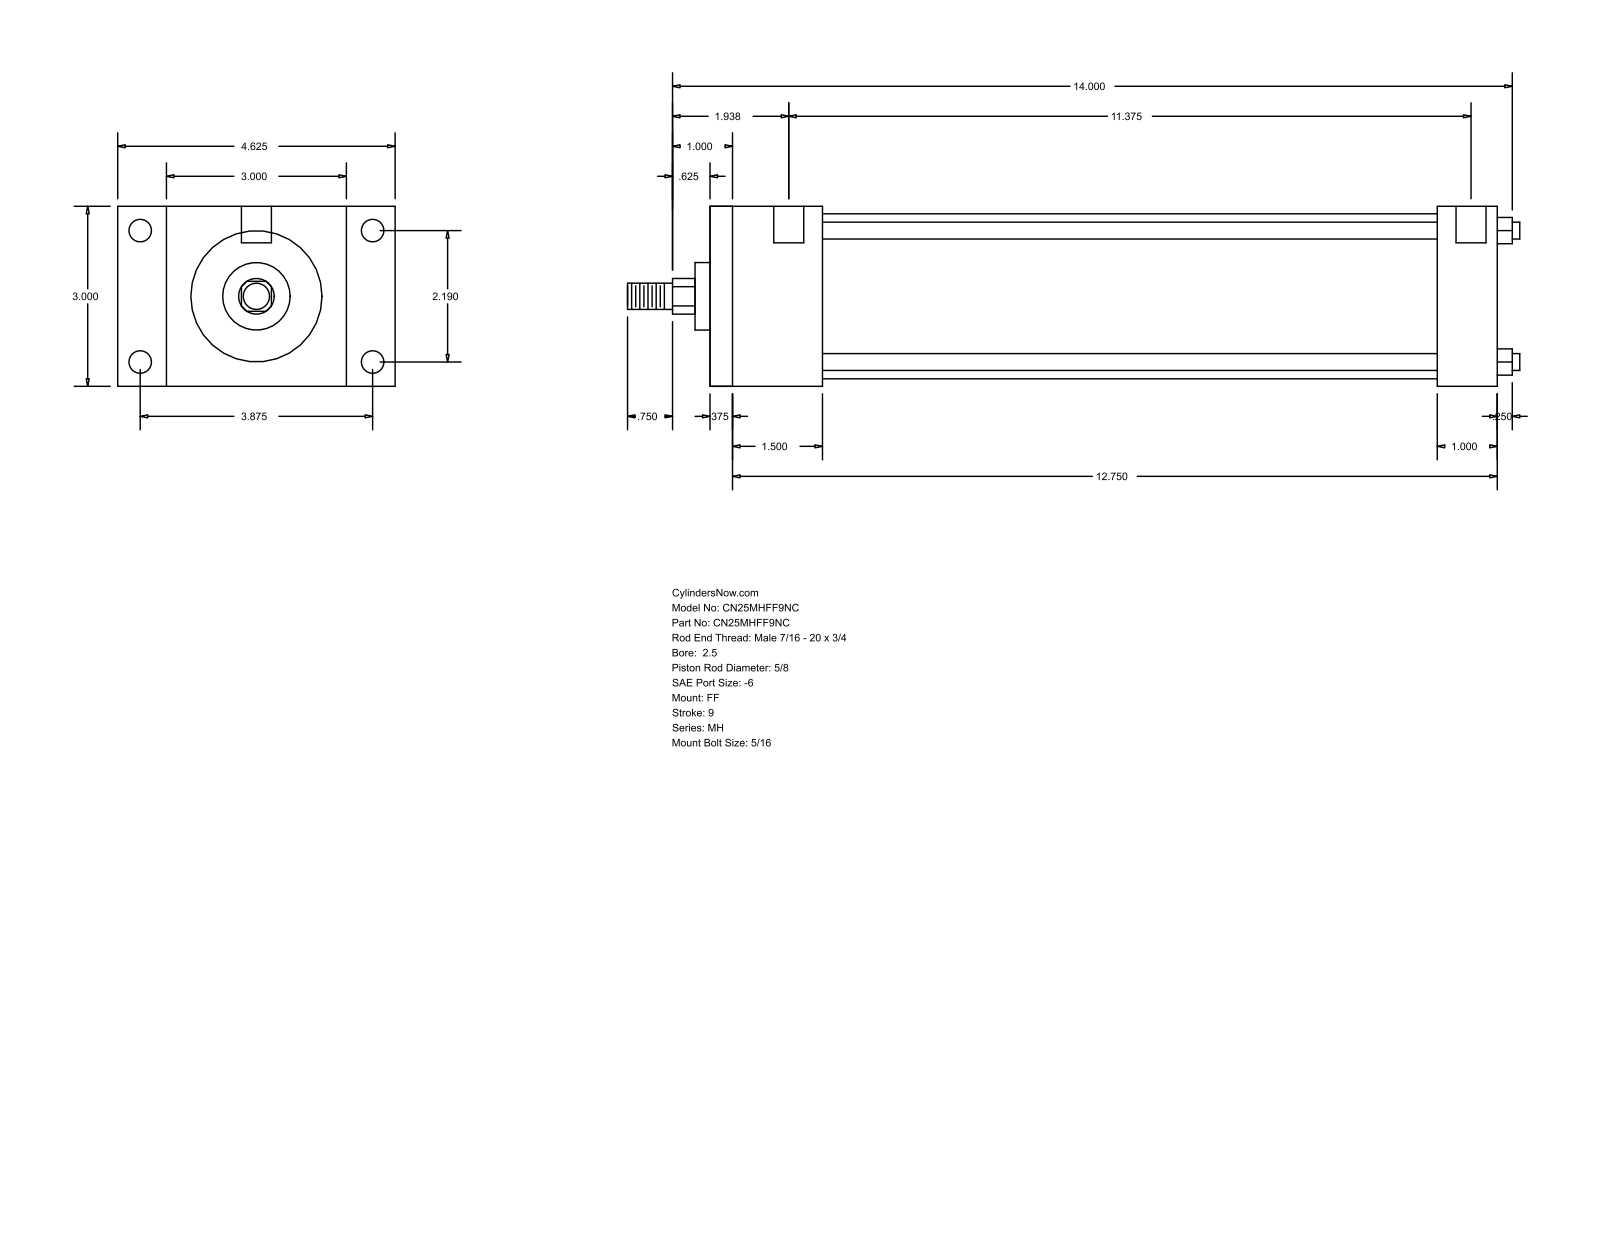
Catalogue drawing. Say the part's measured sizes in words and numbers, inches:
The part is named "MH_FF__0250_0.625". Its 3-D file was written by "GSSL Pune (CONFIG_CONTROL_DESIGN)". It is 0 solids with 92 faces: 64 planar, 28 cylindrical and 0 other. Overall it measures 14.875 by 4.625 by 3 inches. Round holes: 4 of diameter 0.219, 4 of diameter 0.375, 2 of diameter 0.5. Round bosses or shafts: 4 of diameter 0.281, 1 of diameter 2.75, 1 of diameter 1.125, 1 of diameter 0.625, 1 of diameter 0.437. Partial cylindrical surfaces (rounded edges, fillets, slot ends): 1 of radius 0.297. The main face-to-face distances are 3, 13.125, 0.375, 12.75, 1, 1.875, 12.125, 1.5, 11.75, 10.25. The hole center spacings are 2.19, 3.875, 4.451, 11.687, 0.125, 0.187, 11.375, 11.5.
